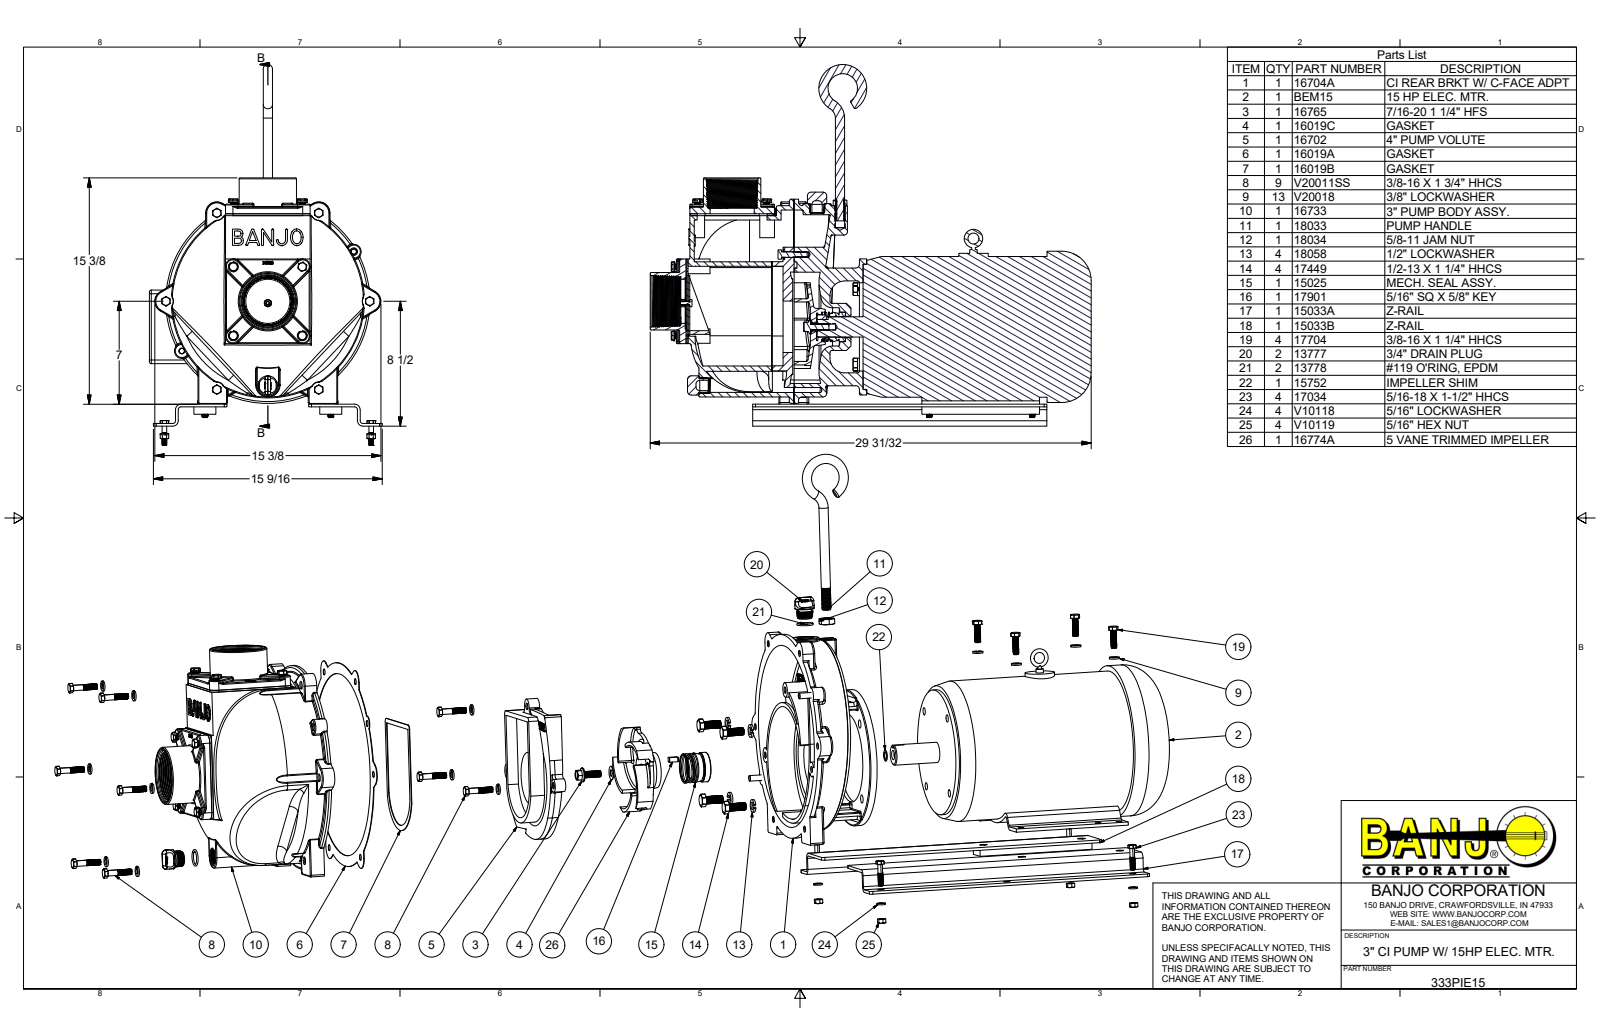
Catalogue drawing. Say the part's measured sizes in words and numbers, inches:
The part is named "333pie15; 16704A; 16704AX; 16020 (+8 more)". Its 3-D file was written by "Autodesk Inventor 2013 (AUTOMOTIVE_DESIGN)". It is 93 solids with 8422 faces: 1366 planar, 3291 cylindrical and 3765 other. Overall it measures 29.983 by 25.893 by 15.83 inches. Its volume is 1 665 cubic inches and its surface area 4 152 square inches. Round holes: 21 of diameter 0.307, 21 of diameter 0.385, 16 of diameter 0.406, 10 of diameter 0.406, 8 of diameter 0.4, 6 of diameter 0.41, 6 of diameter 0.413, 5 of diameter 0.563, 4 of diameter 0.252, 4 of diameter 0.322, 4 of diameter 0.512, 3 of diameter 0.393. Round bosses or shafts: 395 of diameter 0.324, 60 of diameter 0.436, 60 of diameter 0.268, 23 of diameter 0.375, 21 of diameter 0.687, 12 of diameter 0.212, 8 of diameter 1, 5 of diameter 0.5. Partial cylindrical surfaces (rounded edges, fillets, slot ends): 130 of radius 0.06, 102 of radius 0.125, 42 of radius 0.162, 28 of radius 0.25, 26 of radius 0.5, 12 of radius 0.188, 12 of radius 0.322, 10 of radius 0.11. The main face-to-face distances are 0.187, 0.3, 1.313, 1.5, 0.031, 4.686, 0.125, 4.718, 7.315, 7.346. The hole center spacings are 12.008, 6.937, 6.928, 6.933, 12.016, 3.625, 4.875, 5.127.
